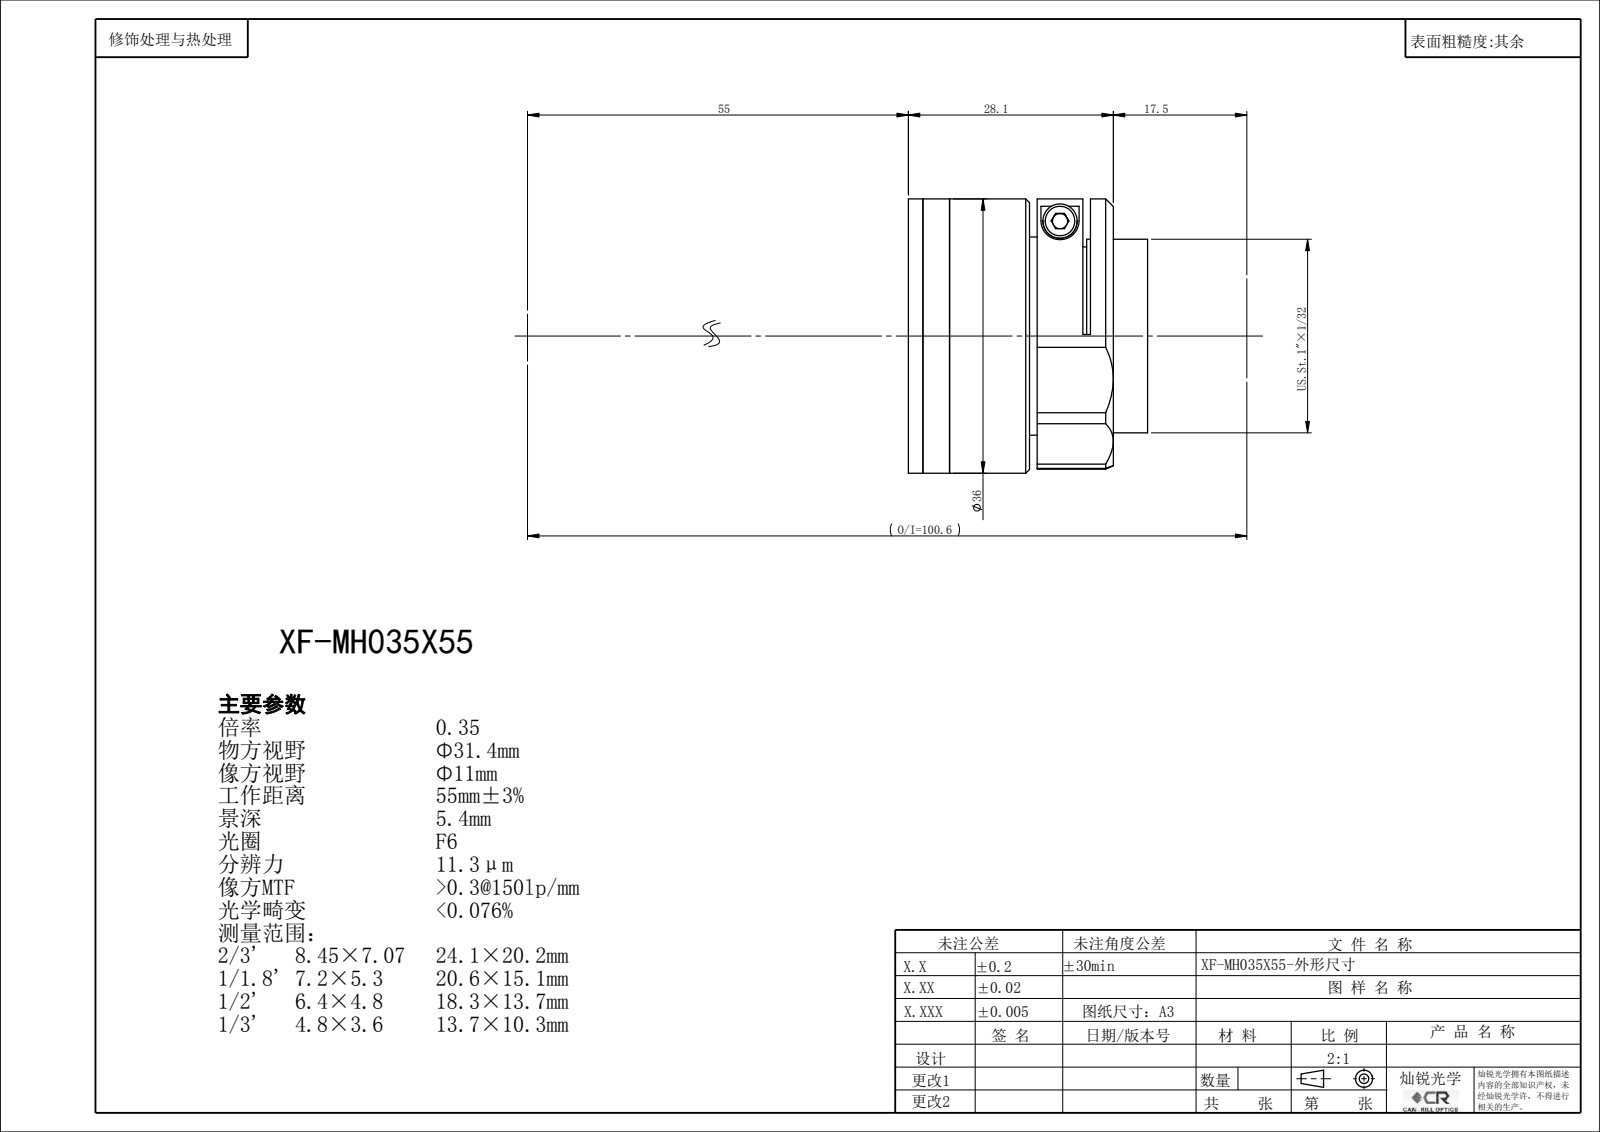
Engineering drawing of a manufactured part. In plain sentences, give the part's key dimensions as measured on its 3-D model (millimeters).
The part is named "XF-MH035X55". Its 3-D file was written by "SolidWorks 2022 (CONFIG_CONTROL_DESIGN)". It is 14 solids with 240 faces: 92 planar, 102 cylindrical and 46 other. Overall it measures 36 by 36 by 32.08 millimeters. Its volume is 20 300 cubic millimeters and its surface area 17 345 square millimeters. Round holes: 3 of diameter 2.5, 1 of diameter 2.85, 1 of diameter 6, 1 of diameter 7, 1 of diameter 7.4, 1 of diameter 8.4, 1 of diameter 10, 1 of diameter 12, 1 of diameter 14, 1 of diameter 16, 1 of diameter 18, 1 of diameter 20. Round bosses or shafts: 3 of diameter 3, 1 of diameter 36, 1 of diameter 34, 1 of diameter 28, 1 of diameter 27, 1 of diameter 25.4, 1 of diameter 9, 1 of diameter 8. The main face-to-face distances are 5, 8, 1.91, 26.17, 21.17, 6.91, 28.08, 16.67, 3, 4.
